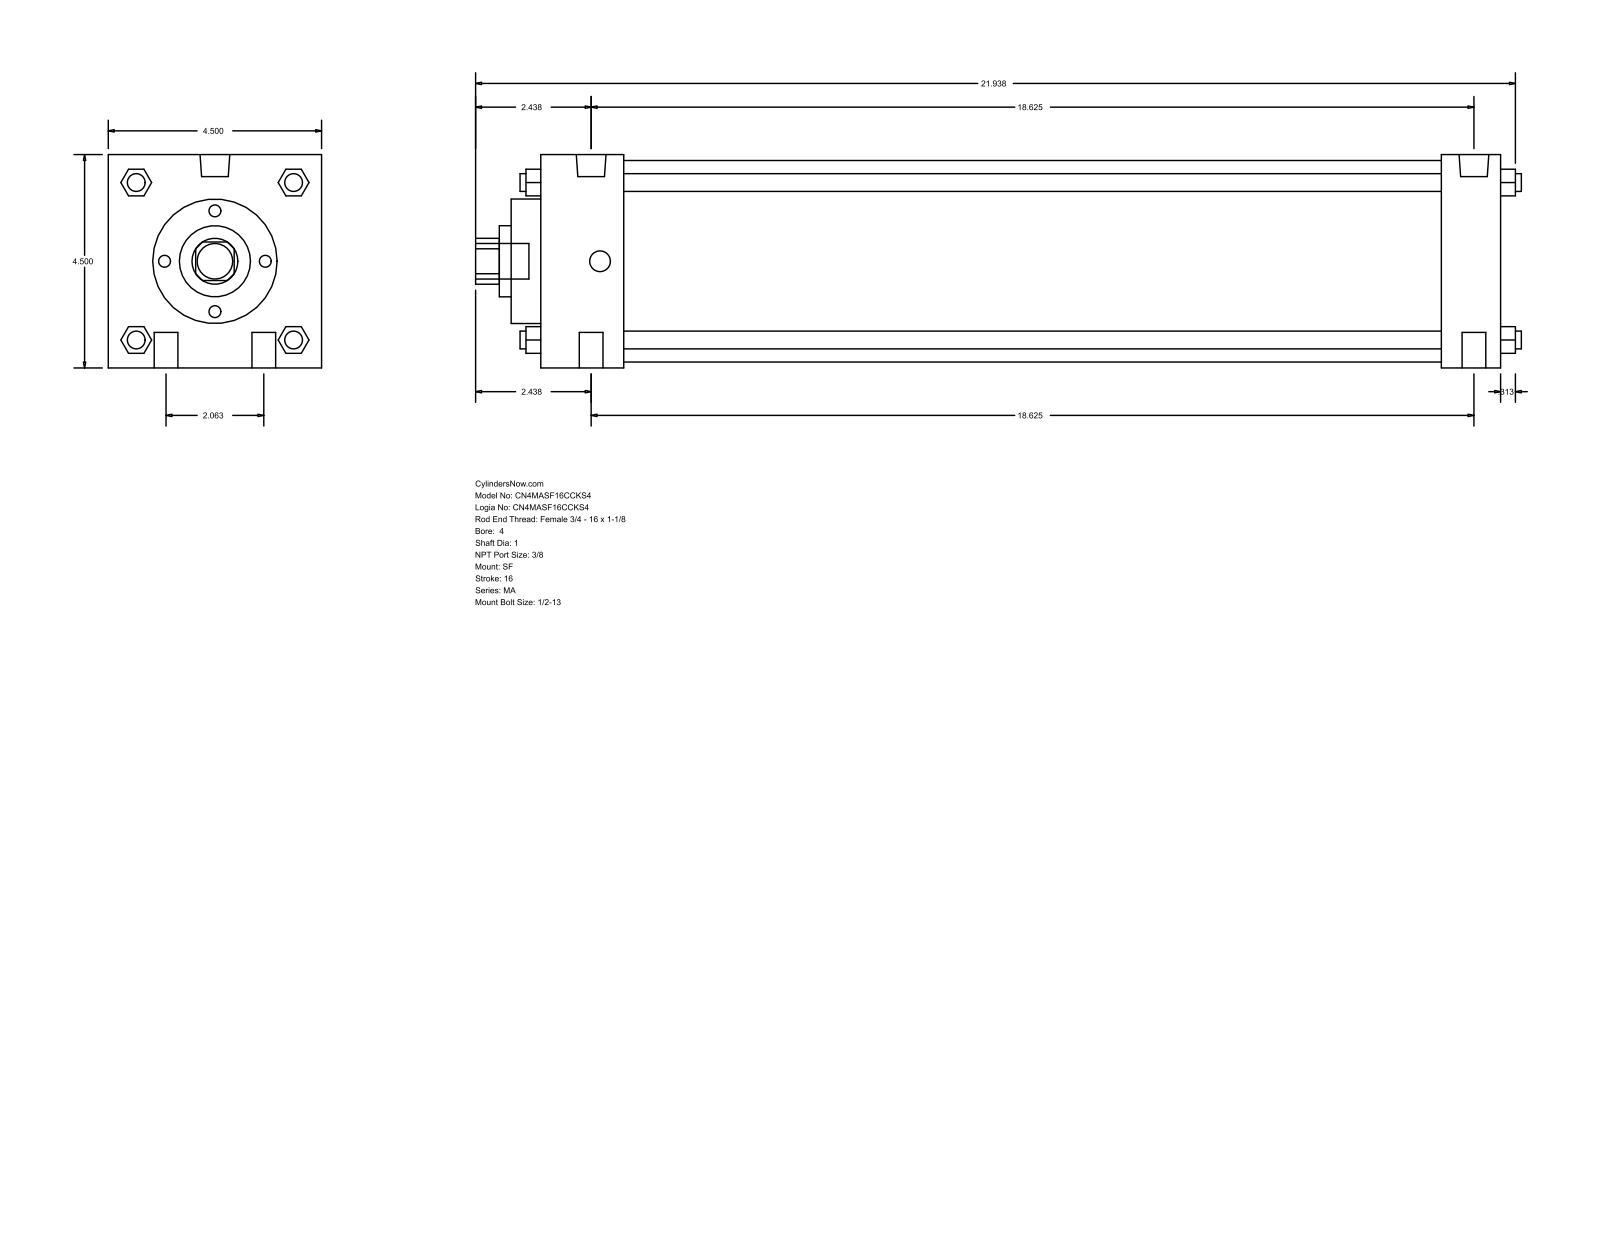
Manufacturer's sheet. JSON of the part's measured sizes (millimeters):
{"part_name": "MA_SF__0400_1", "step_written_by": "GSSL Pune (CONFIG_CONTROL_DESIGN)", "units": "millimeters", "bodies": {"solids": 0, "faces": 126, "planar": 95, "cylindrical": 31, "other": 0}, "overall_size": [560.39, 114.3, 114.3], "round_holes": [[25.4, 1], [38.1, 1], [66.67, 1], [107.95, 1]], "round_bosses_or_shafts": [[12.7, 4], [9.53, 4], [15.93, 2], [11.11, 2], [19.05, 1]], "partial_cylinders_radius": [[12.29, 1]], "face_to_face_distances": [114.3, 514.35, 482.6, 31.75, 44.46, 438.14, 469.89, 530.22, 15.87, 60.33]}
